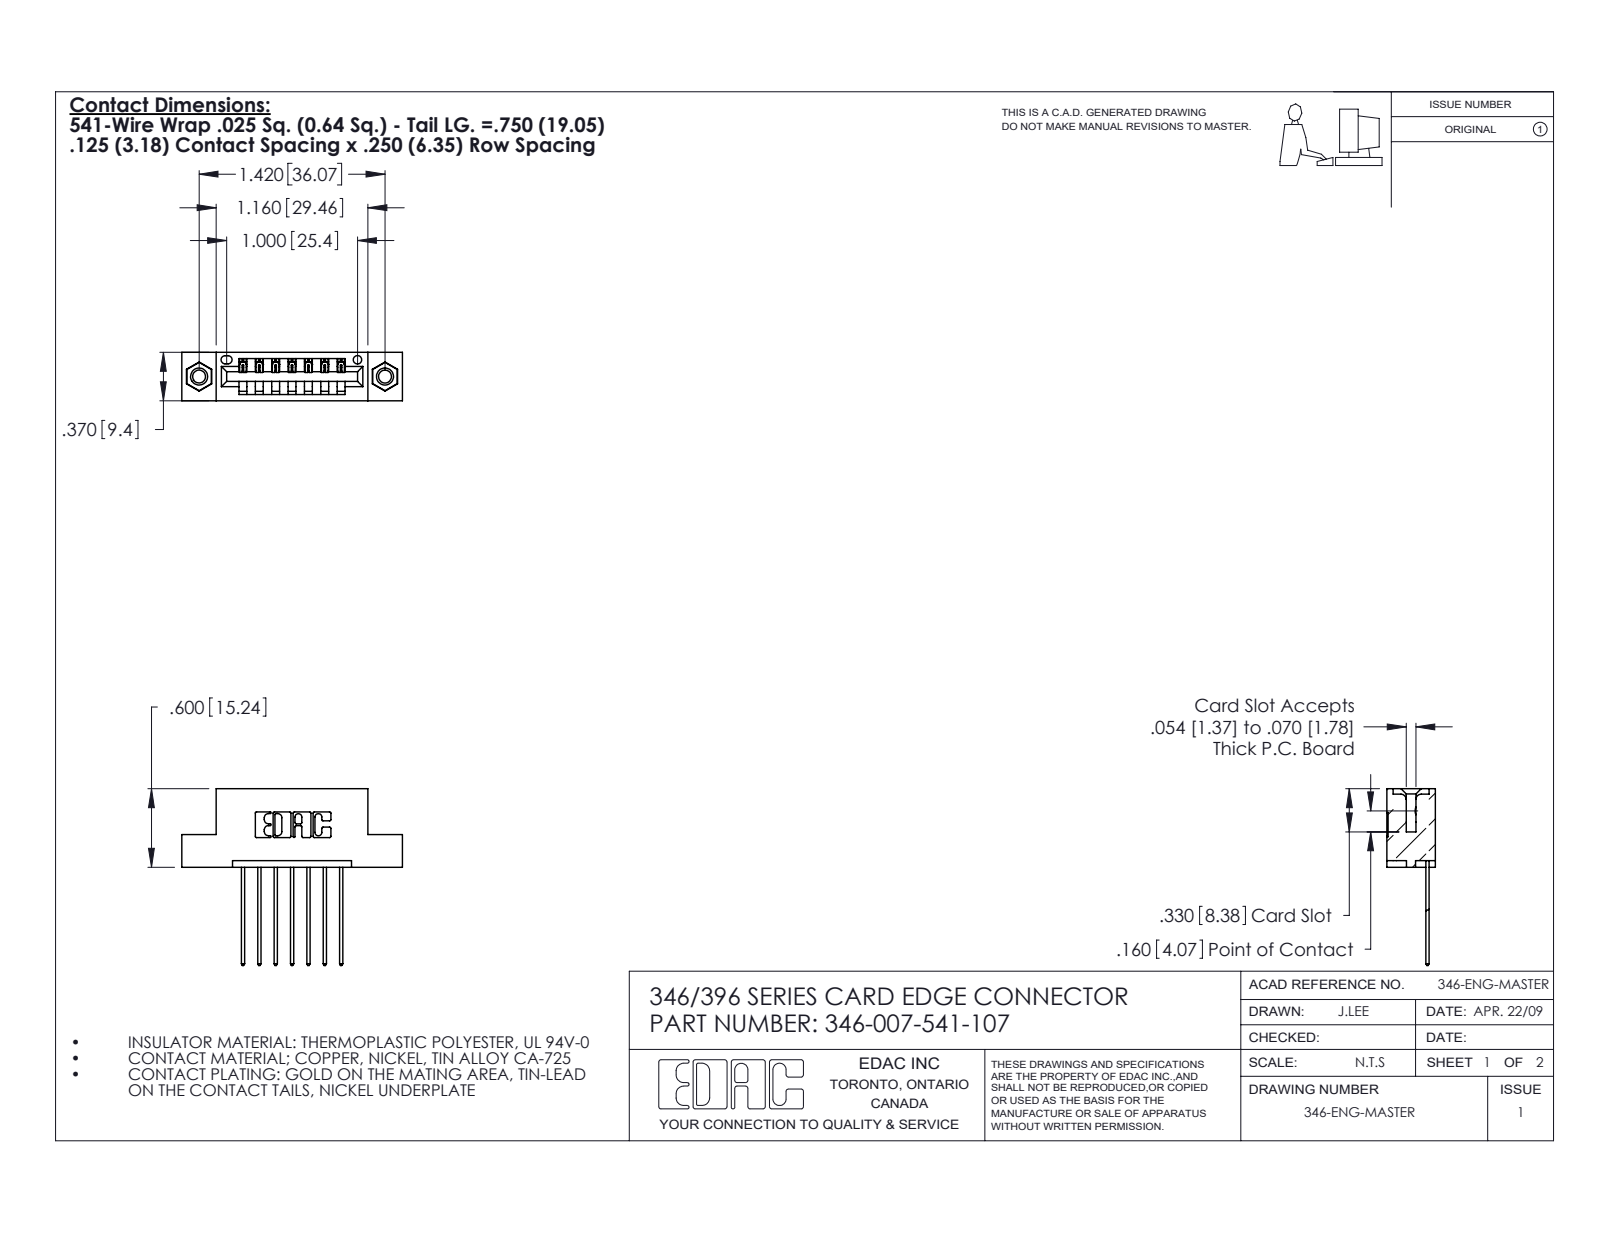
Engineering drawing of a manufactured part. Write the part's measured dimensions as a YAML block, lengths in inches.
part_name: "345-292-001_345-293-141; 346-007-541-107; 346 Part_Flush Mounting Lugs - 0.156 Dia-TI; 345-250-001_345-250-005-103"
step_written_by: "SolidWorks 2020 (CONFIG_CONTROL_DESIGN)"
units: inches
bodies: {solids: 10, faces: 588, planar: 388, cylindrical: 184, other: 16}
overall_size: [1.685, 1.35, 0.37]
volume: 0.236
surface_area: 7.17
round_holes:
  - {diameter: 0.098, count: 2}
  - {diameter: 0.125, count: 2}
  - {diameter: 0.156, count: 2}
  - {diameter: 0.064, count: 1}
round_bosses_or_shafts:
  - {diameter: 0.155, count: 2}
partial_cylinders:
  - {radius: 0.01, count: 22}
  - {radius: 0.006, count: 14}
  - {radius: 0.01, count: 14}
  - {radius: 0.007, count: 6}
  - {radius: 0.031, count: 6}
  - {radius: 0.026, count: 3}
  - {radius: 0.031, count: 2}
  - {radius: 0.04, count: 2}
face_to_face_distances: [0.25, 0.048, 0.322, 0.37, 0.072, 0.298, 0.025, 0.148, 0.222, 0.1]
hole_center_spacings: [0.246, 1.217, 1.42]
